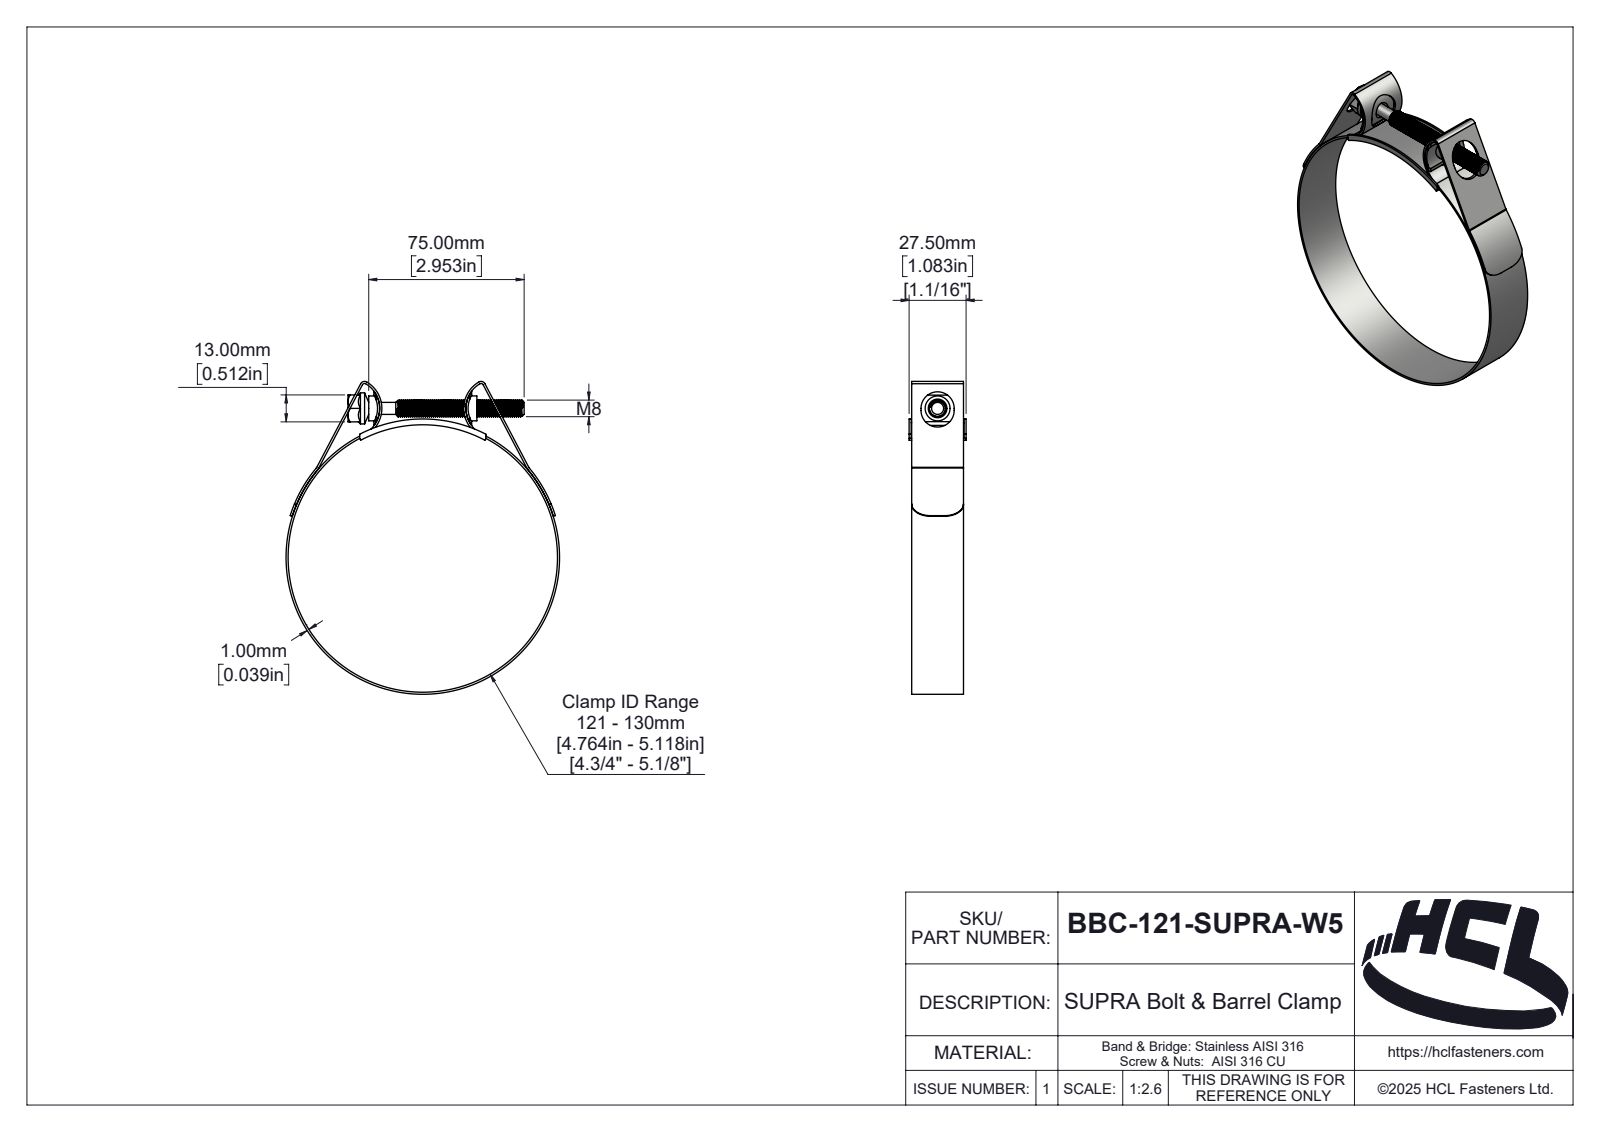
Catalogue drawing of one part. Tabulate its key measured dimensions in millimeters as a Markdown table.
| quantity | value |
| --- | --- |
| part name | BBC-121-SUPRA-W5 |
| STEP written by | SolidWorks 2025 (AUTOMOTIVE_DESIGN) |
| units | millimeters |
| bodies | 5 solids, 365 faces (46 planar, 233 cylindrical, 86 other) |
| overall size | 150.92 × 132 × 27.5 |
| volume | 20 699 mm³ |
| surface area | 37 073 mm² |
| round holes (diameter × count) | 130 × 1 |
| round bosses / shafts (diameter × count) | 132 × 1, 15.01 × 1, 12 × 1, 8 × 1, 5.8 × 1 |
| partial cylindrical surfaces (radius × count) | 1 × 4, 1.1 × 2, 2 × 2, 2.1 × 2, 3 × 2, 8 × 2, 12.65 × 2, 13.65 × 2 |
| main face-to-face distances | 1, 25, 1.25, 26.25, 26.5, 25.25, 27.5, 25.5, 13, 2.5 |
